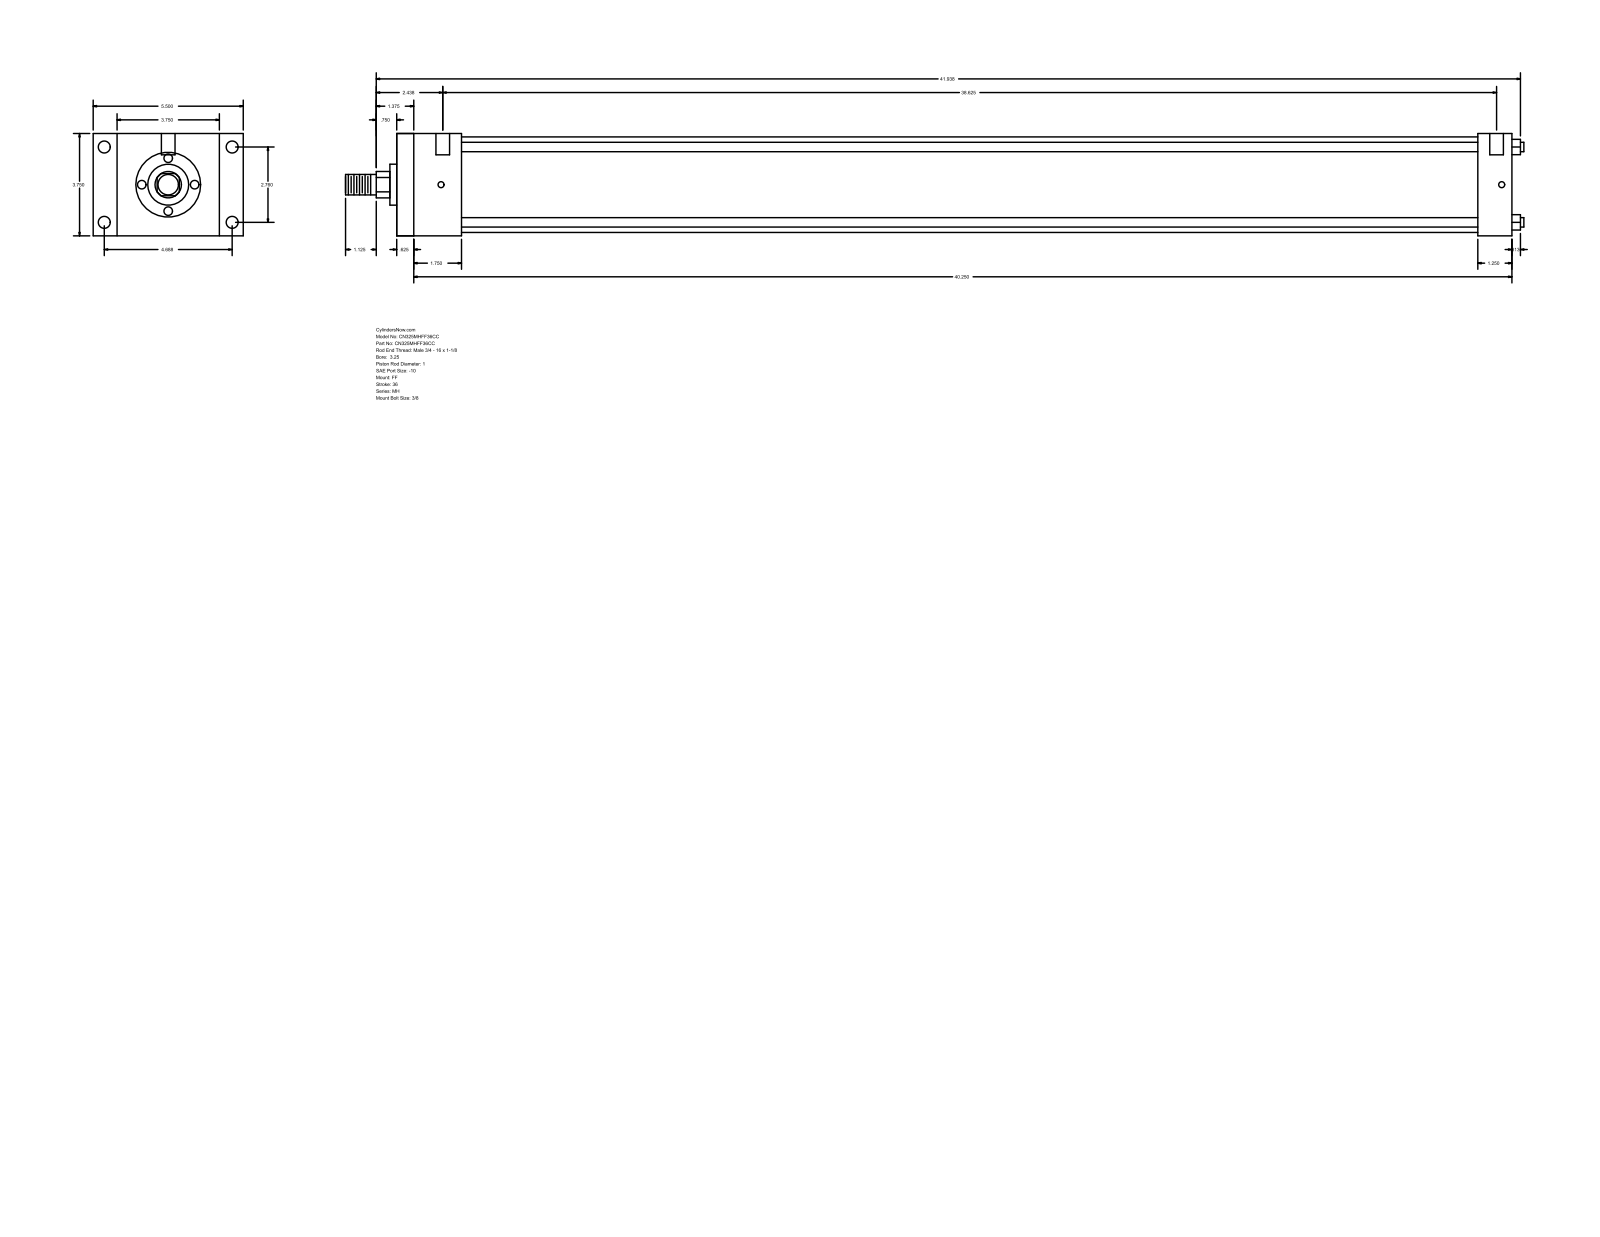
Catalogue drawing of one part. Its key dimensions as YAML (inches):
part_name: "MH_FF__0325_1"
step_written_by: "GSSL Pune (CONFIG_CONTROL_DESIGN)"
units: inches
bodies: {solids: 0, faces: 92, planar: 64, cylindrical: 28, other: 0}
overall_size: [43.187, 5.5, 3.75]
round_holes:
  - {diameter: 0.219, count: 4}
  - {diameter: 0.438, count: 4}
  - {diameter: 0.5, count: 2}
round_bosses_or_shafts:
  - {diameter: 0.345, count: 4}
  - {diameter: 3.5, count: 1}
  - {diameter: 1.5, count: 1}
  - {diameter: 1, count: 1}
  - {diameter: 0.75, count: 1}
partial_cylinders:
  - {radius: 0.484, count: 1}
face_to_face_distances: [3.75, 40.875, 0.625, 40.25, 0.875, 4.625, 39.625, 39, 1.25, 2.375]
hole_center_spacings: [2.76, 4.687, 5.439, 38.875, 0.062, 0.187, 38.625, 38.687]
